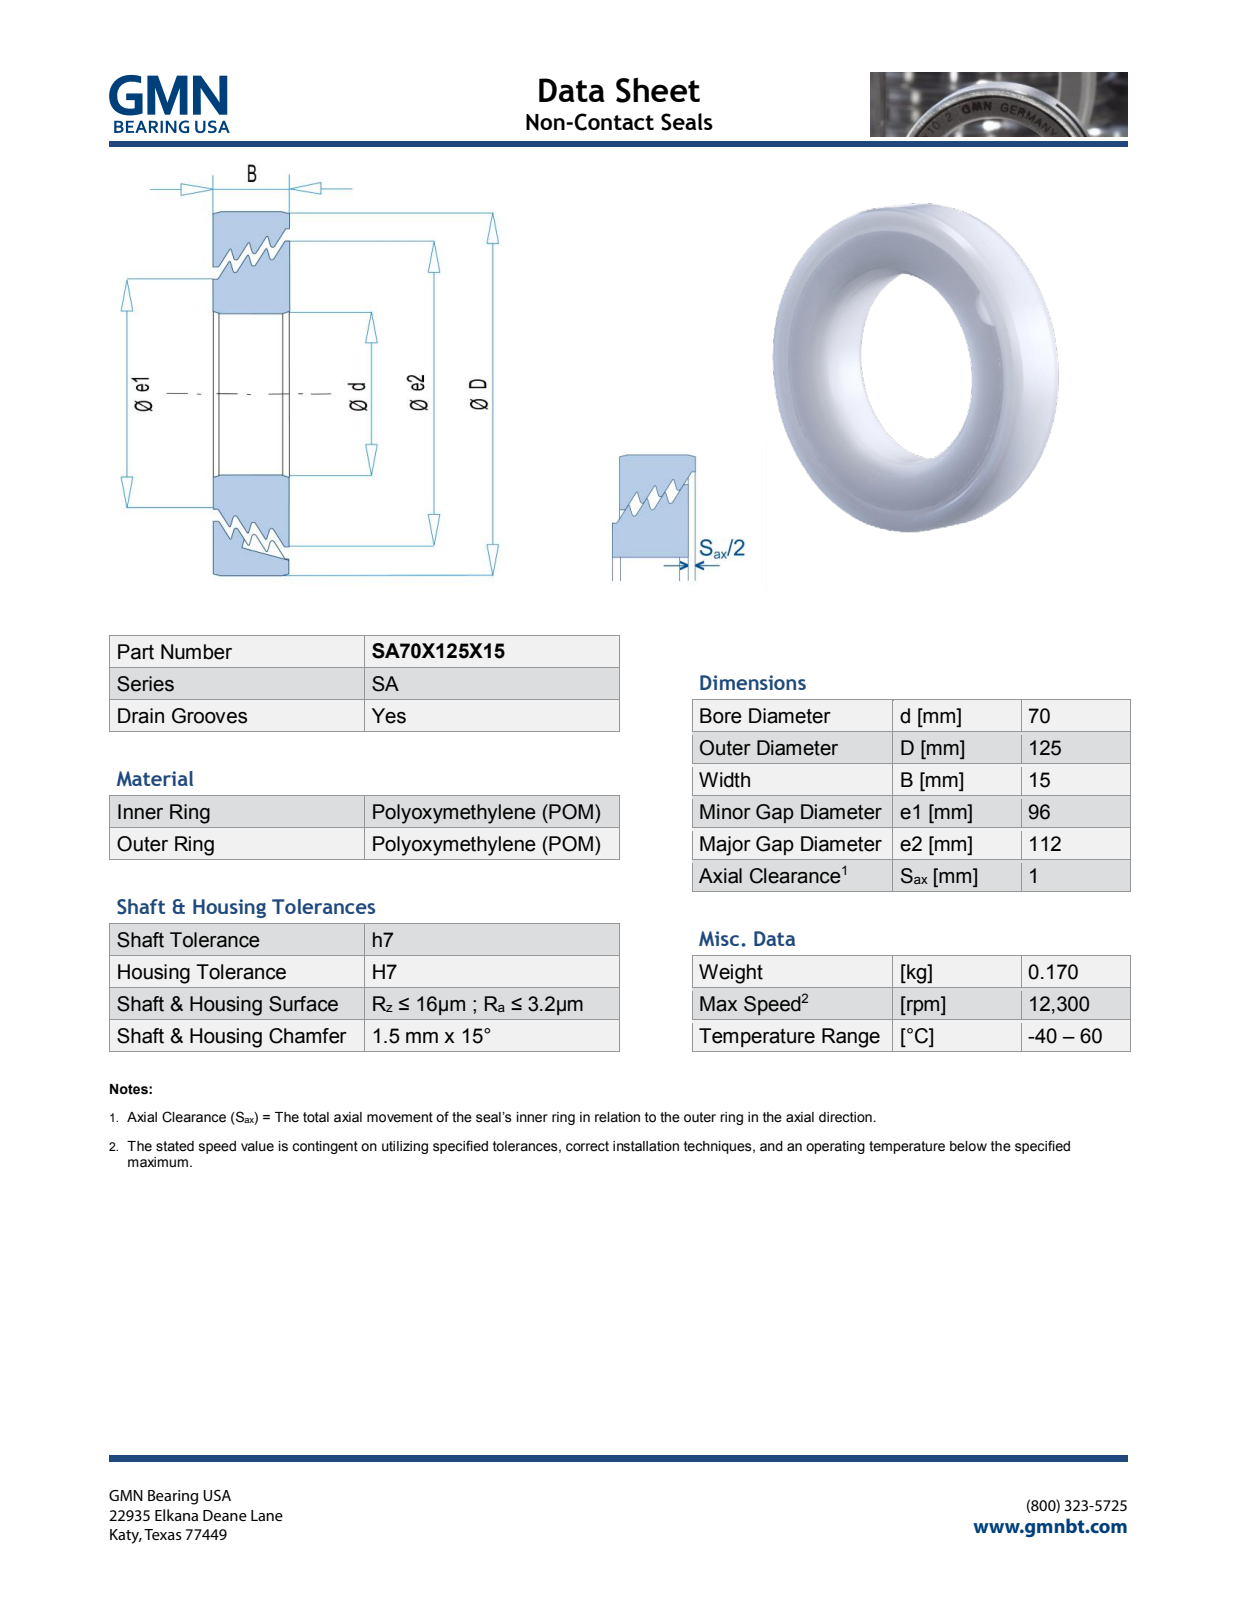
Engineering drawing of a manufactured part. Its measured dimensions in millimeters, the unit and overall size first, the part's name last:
Units: millimetres
Overall size (bounding box): 125 × 125 × 15.07
Round holes (diameter × count): ⌀70 ×1, ⌀97.63 ×1, ⌀113.63 ×1
Round bosses / shafts (diameter × count): ⌀125 ×1, ⌀112 ×1, ⌀96 ×1
Partial cylindrical surfaces — rounded edges, fillets, slot ends (radius × count): R6 ×1
Main face-to-face distances: 15, 15.07, 9.26, 9.19, 5.81, 0.64, 5.15, 0.65, 0.55, 0.58
Volume: 120 830 mm³ · Surface area: 42 967 mm²
Bodies: 2 solids, 639 faces (554 planar, 13 cylindrical, 72 other)
Part name (STEP PRODUCT): SA70X125X15_PRT
STEP written by: PRO/ENGINEER BY PARAMETRIC TECHNOLOGY CORPORATION, 2013150 (AUTOMOTIVE_DESIGN)
